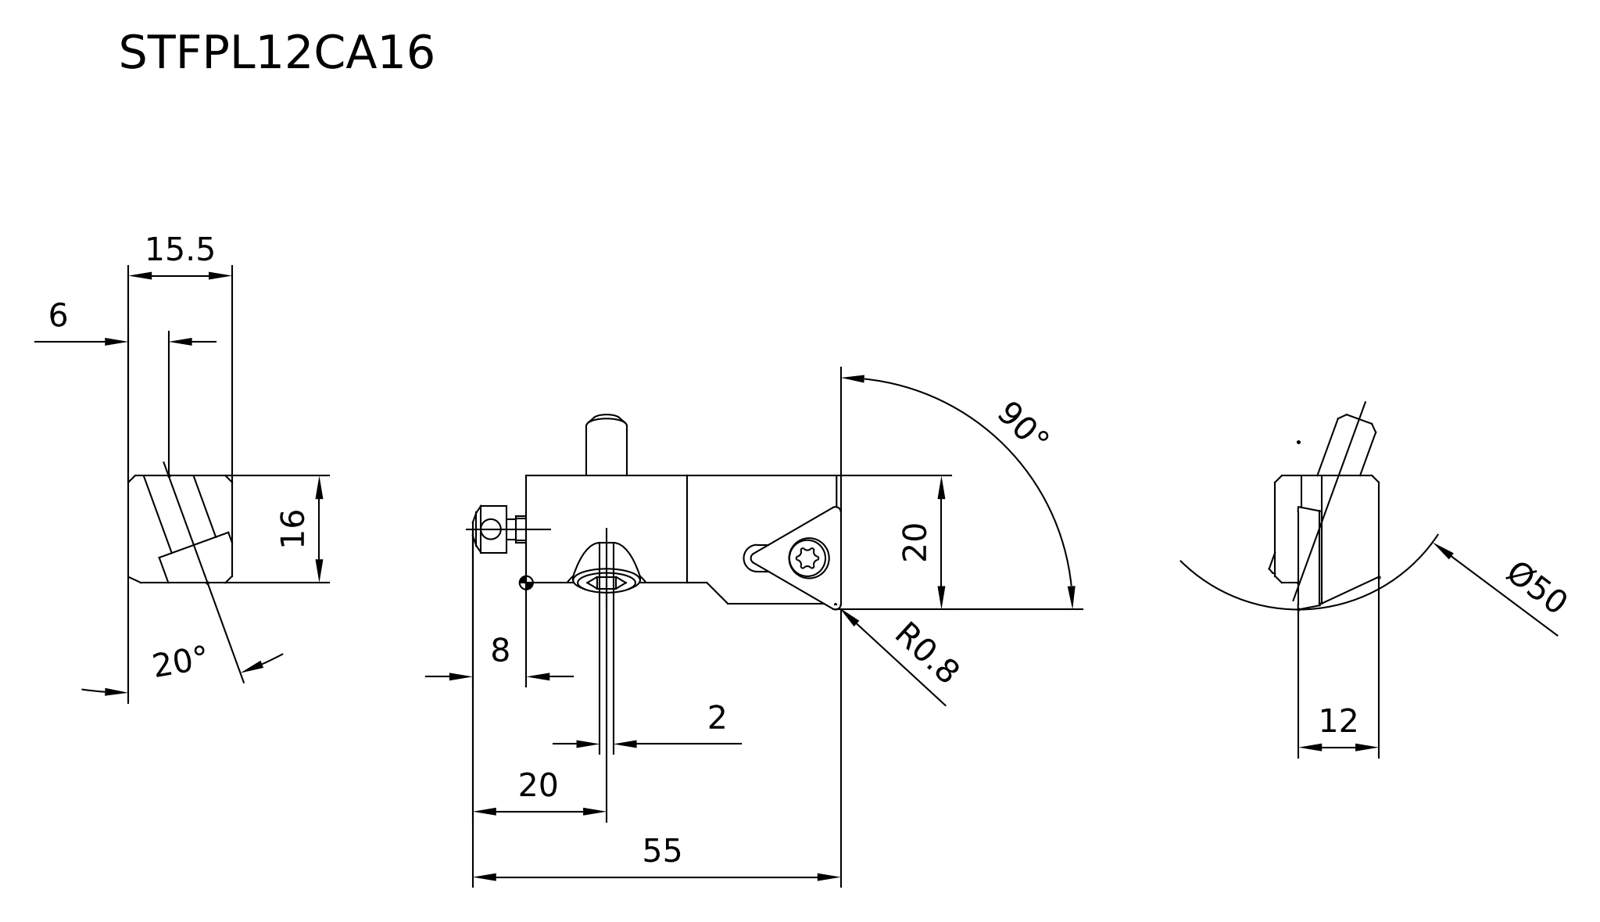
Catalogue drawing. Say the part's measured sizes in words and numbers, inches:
The part is named "STFPL12CA16_ASM". Its 3-D file was written by "SIEMENS PLM Software NX 10.0 (AUTOMOTIVE_DESIGN)". It is 5 solids with 141 faces: 49 planar, 60 cylindrical and 32 other. Overall it measures 2.14 by 1.11 by 0.645 inches. Its volume is 0.585 cubic inches and its surface area 8.251 square inches. Round holes: 2 of diameter 0.071, 2 of diameter 0.13, 1 of diameter 0.197. Round bosses or shafts: 2 of diameter 0.236, 2 of diameter 0.157, 1 of diameter 0.394, 1 of diameter 0.276, 1 of diameter 0.213, 1 of diameter 0.118. Partial cylindrical surfaces (rounded edges, fillets, slot ends): 6 of radius 0.011, 6 of radius 0.013, 6 of radius 0.026, 6 of radius 0.033, 2 of radius 0.138, 2 of radius 0.217, 1 of radius 0.079, 1 of radius 0.394. The main face-to-face distances are 0.61, 0.63, 0.106, 0.118, 0.236, 0.751, 0.121, 0.276, 0.821, 0.197. The hole center spacings are 1.647.
